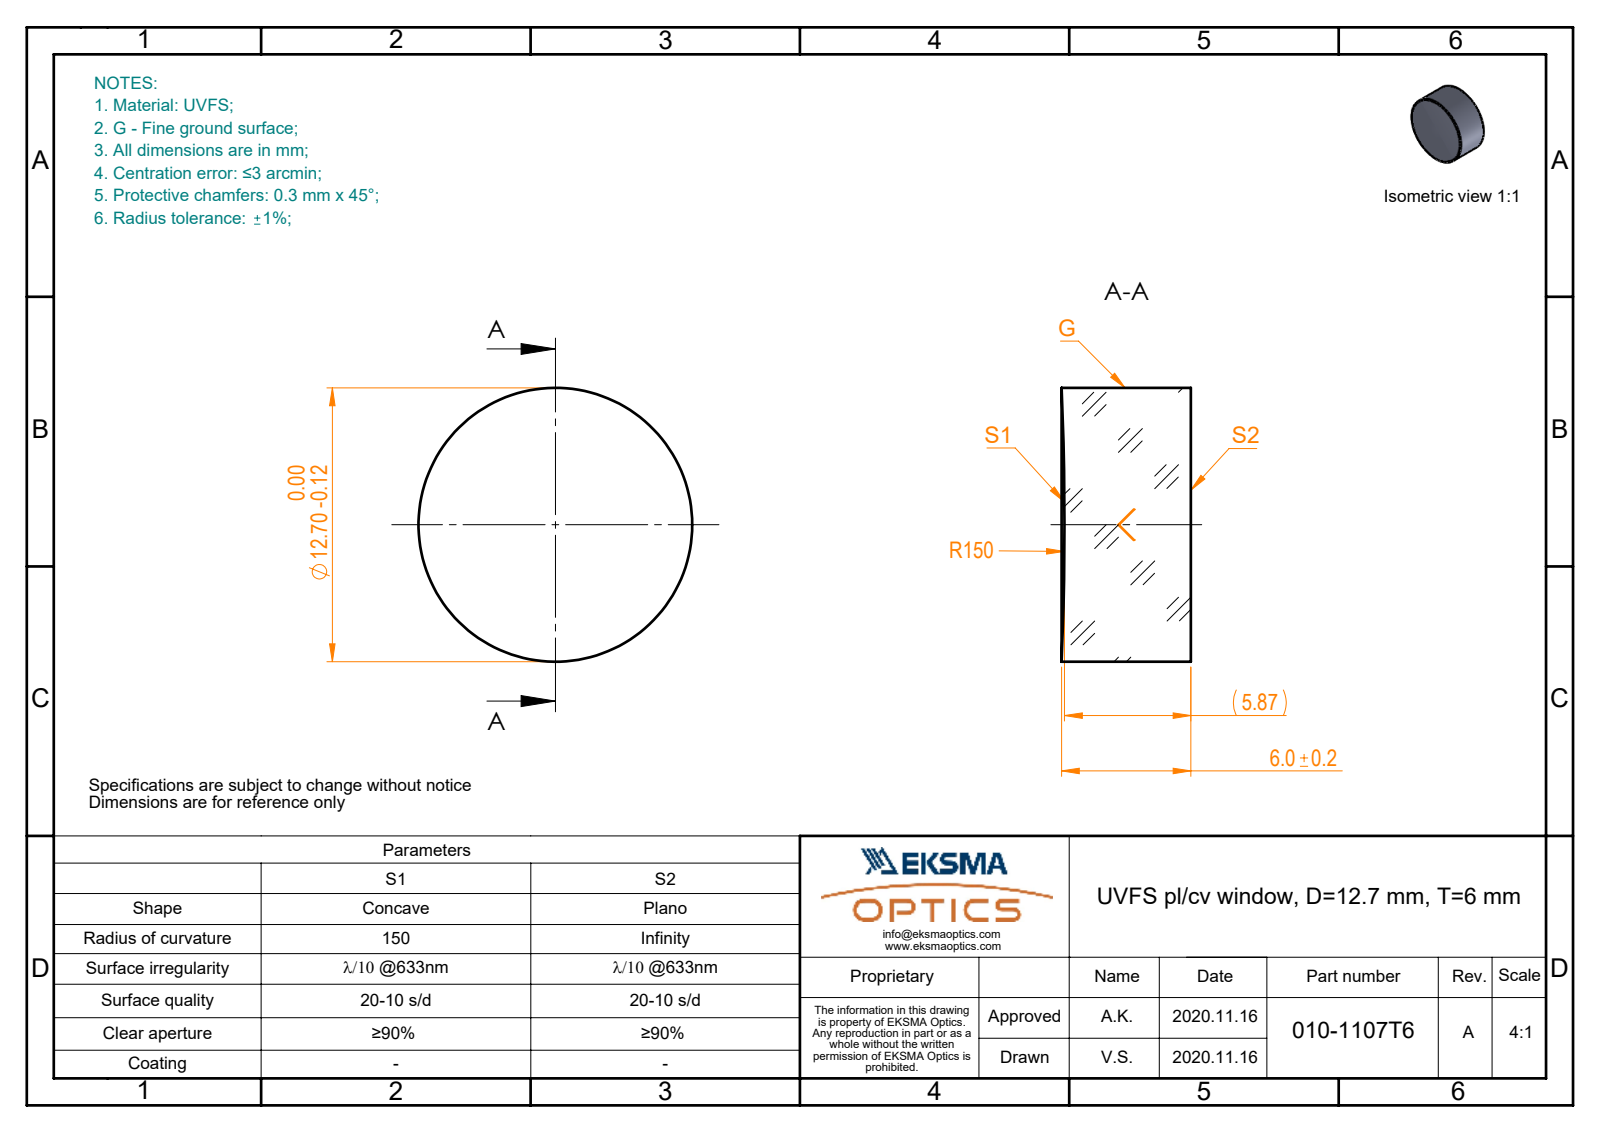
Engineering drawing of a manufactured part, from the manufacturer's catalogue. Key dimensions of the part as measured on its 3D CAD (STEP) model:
Part name (STEP PRODUCT): 010-1107T6_UVFS_PCV_window
STEP written by: SolidWorks 2019 (CONFIG_CONTROL_DESIGN)
Units: millimetres
Bodies: 1 solid, 5 faces (1 planar, 2 cylindrical, 2 other)
Overall size (bounding box): 12.7 × 12.7 × 6
Volume: 752 mm³ · Surface area: 493 mm²
Round bosses / shafts (diameter × count): ⌀12.7 ×1
